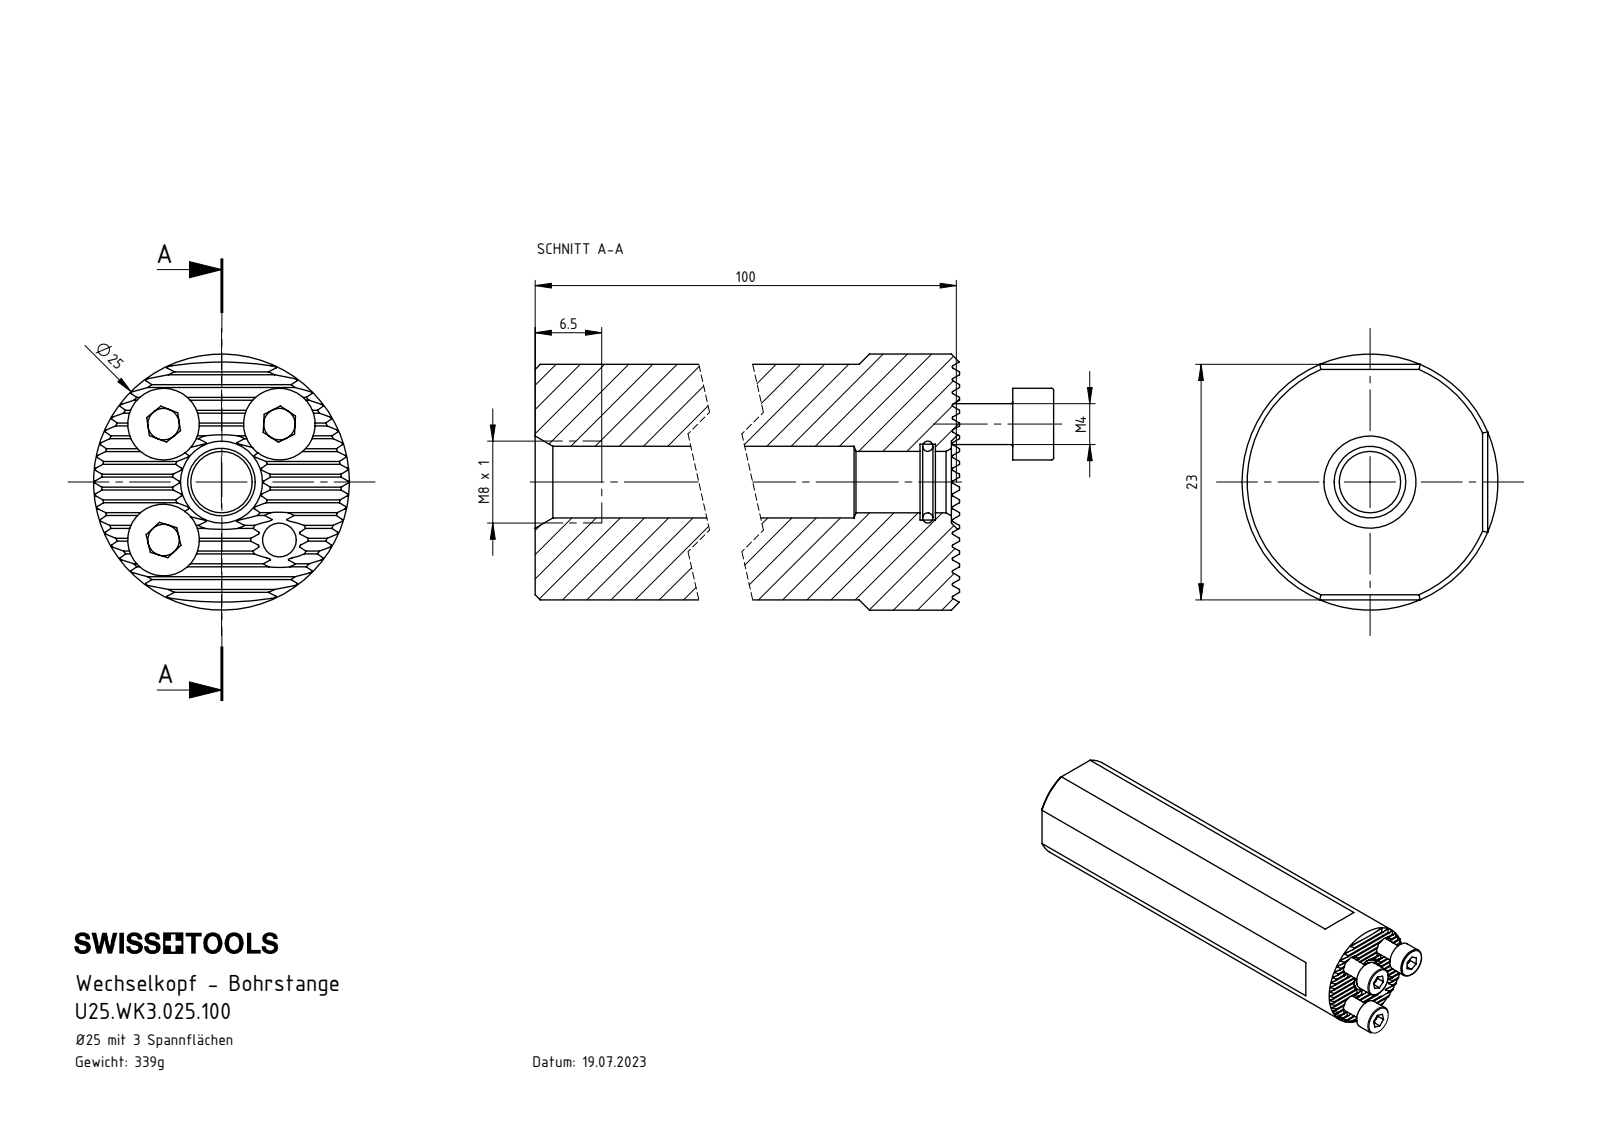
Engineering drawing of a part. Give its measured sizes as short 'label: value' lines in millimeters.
name: ISO 4762 - M4 x 12; U25-WK3.025.100_A; U25.WK3.025.100; DIN 3771 - 6x1
written by: SolidWorks 2017 (AUTOMOTIVE_DESIGN)
unit: mm
bodies: 5 solids, 318 faces (188 planar, 72 cylindrical, 58 other)
size: 109.5 × 25 × 25
volume: 43 923 mm³; area: 12 542 mm²
holes: 4× ⌀3.3, 1× ⌀6, 1× ⌀7, 1× ⌀7.4
bosses: 3× ⌀7, 3× ⌀4, 1× ⌀25
rounds: 19× R0.12
face distances: 23, 4.33, 1.08, 3.25, 8.66, 5.41, 7.58, 2.16, 2.17, 9.74
hole spacings: 8, 11.32, 16.01
